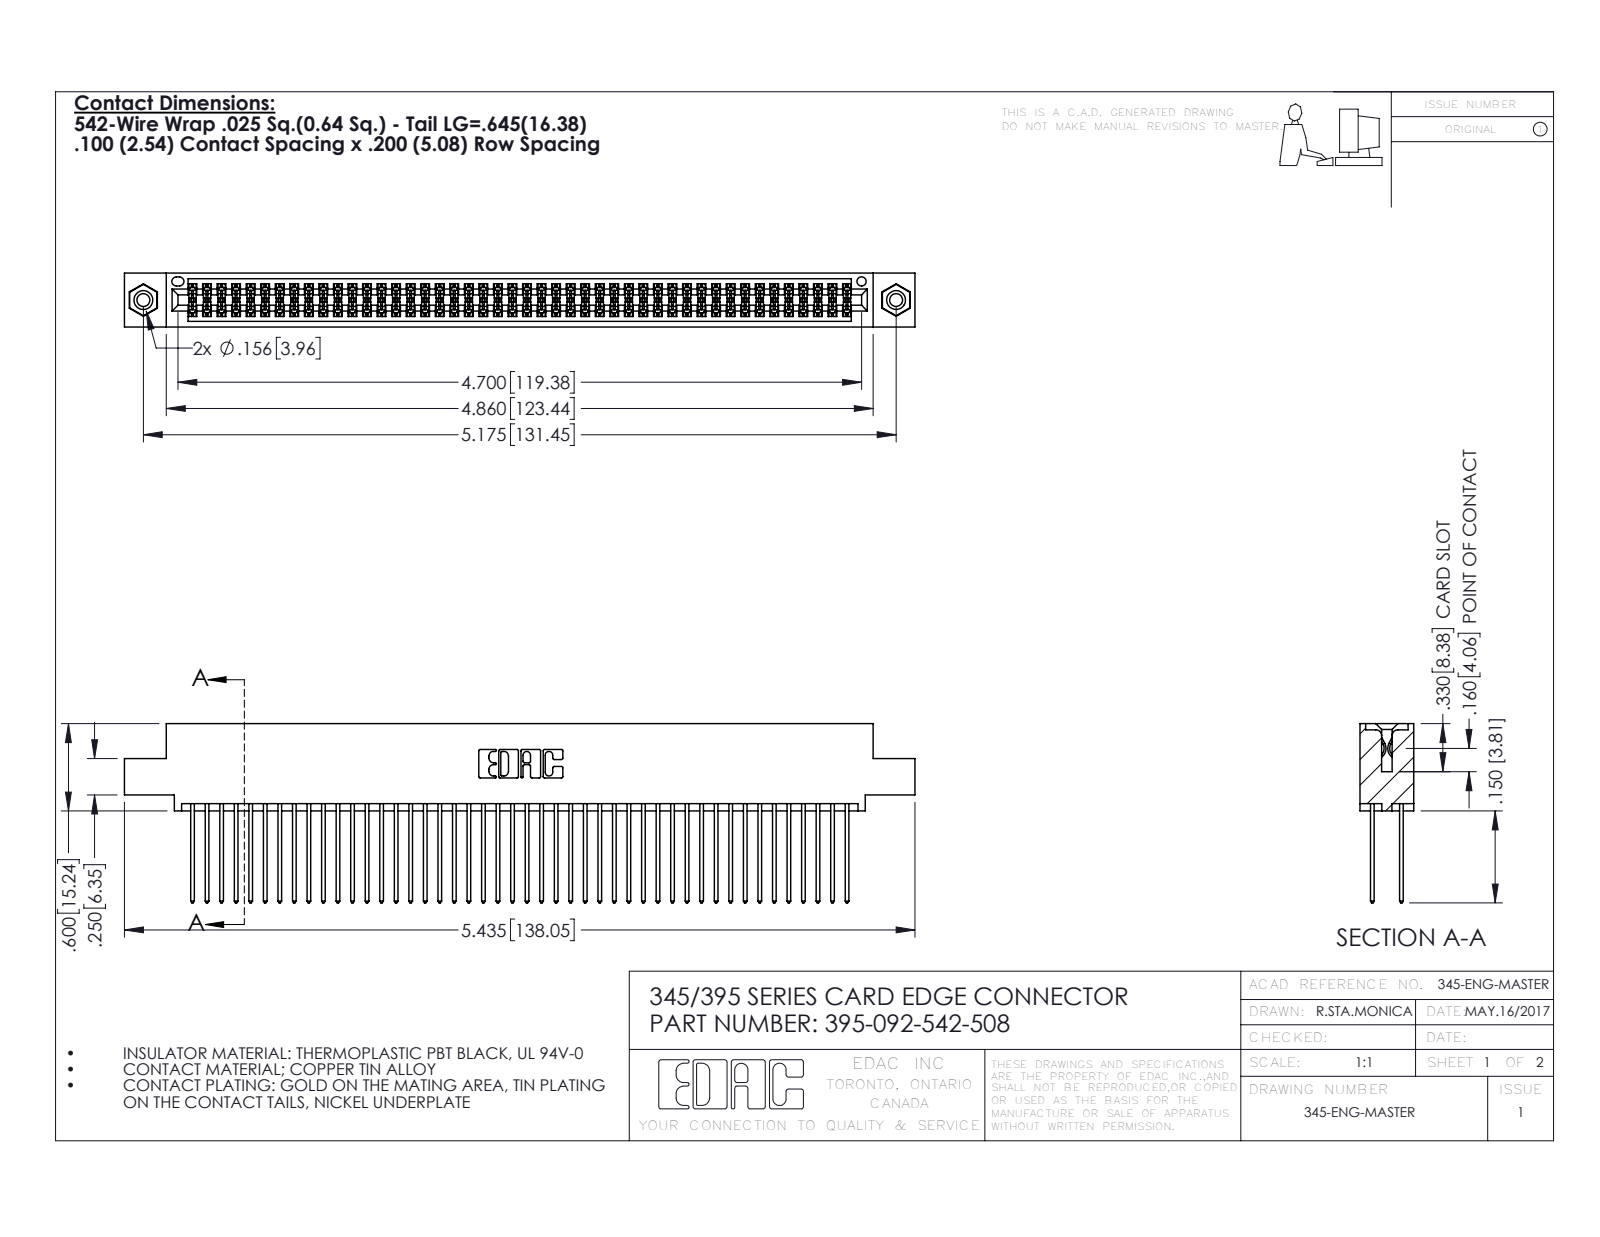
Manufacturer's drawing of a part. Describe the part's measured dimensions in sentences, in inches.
The part is named "345-250-001_345-250-003-102; 345 Part_0.110 Offset - 0.156 Dia-TI; 345-292-001_345-293-142; 395-092-542-508". Its 3-D file was written by "SolidWorks 2016 (CONFIG_CONTROL_DESIGN)". It is 95 solids with 4790 faces: 3152 planar, 1622 cylindrical and 16 other. Overall it measures 5.435 by 1.232 by 0.37 inches. Its volume is 0.842 cubic inches and its surface area 35 square inches. Round holes: 2 of diameter 0.089, 2 of diameter 0.125, 2 of diameter 0.156, 1 of diameter 0.064. Round bosses or shafts: 2 of diameter 0.155. Partial cylindrical surfaces (rounded edges, fillets, slot ends): 138 of radius 0.006, 92 of radius 0.01, 22 of radius 0.01, 6 of radius 0.007, 6 of radius 0.031, 3 of radius 0.026, 2 of radius 0.014, 2 of radius 0.019. The main face-to-face distances are 0.072, 0.298, 0.2, 0.098, 0.272, 0.025, 0.225, 0.37, 0.175, 0.149. The hole center spacings are 0.27, 4.939, 5.175.
